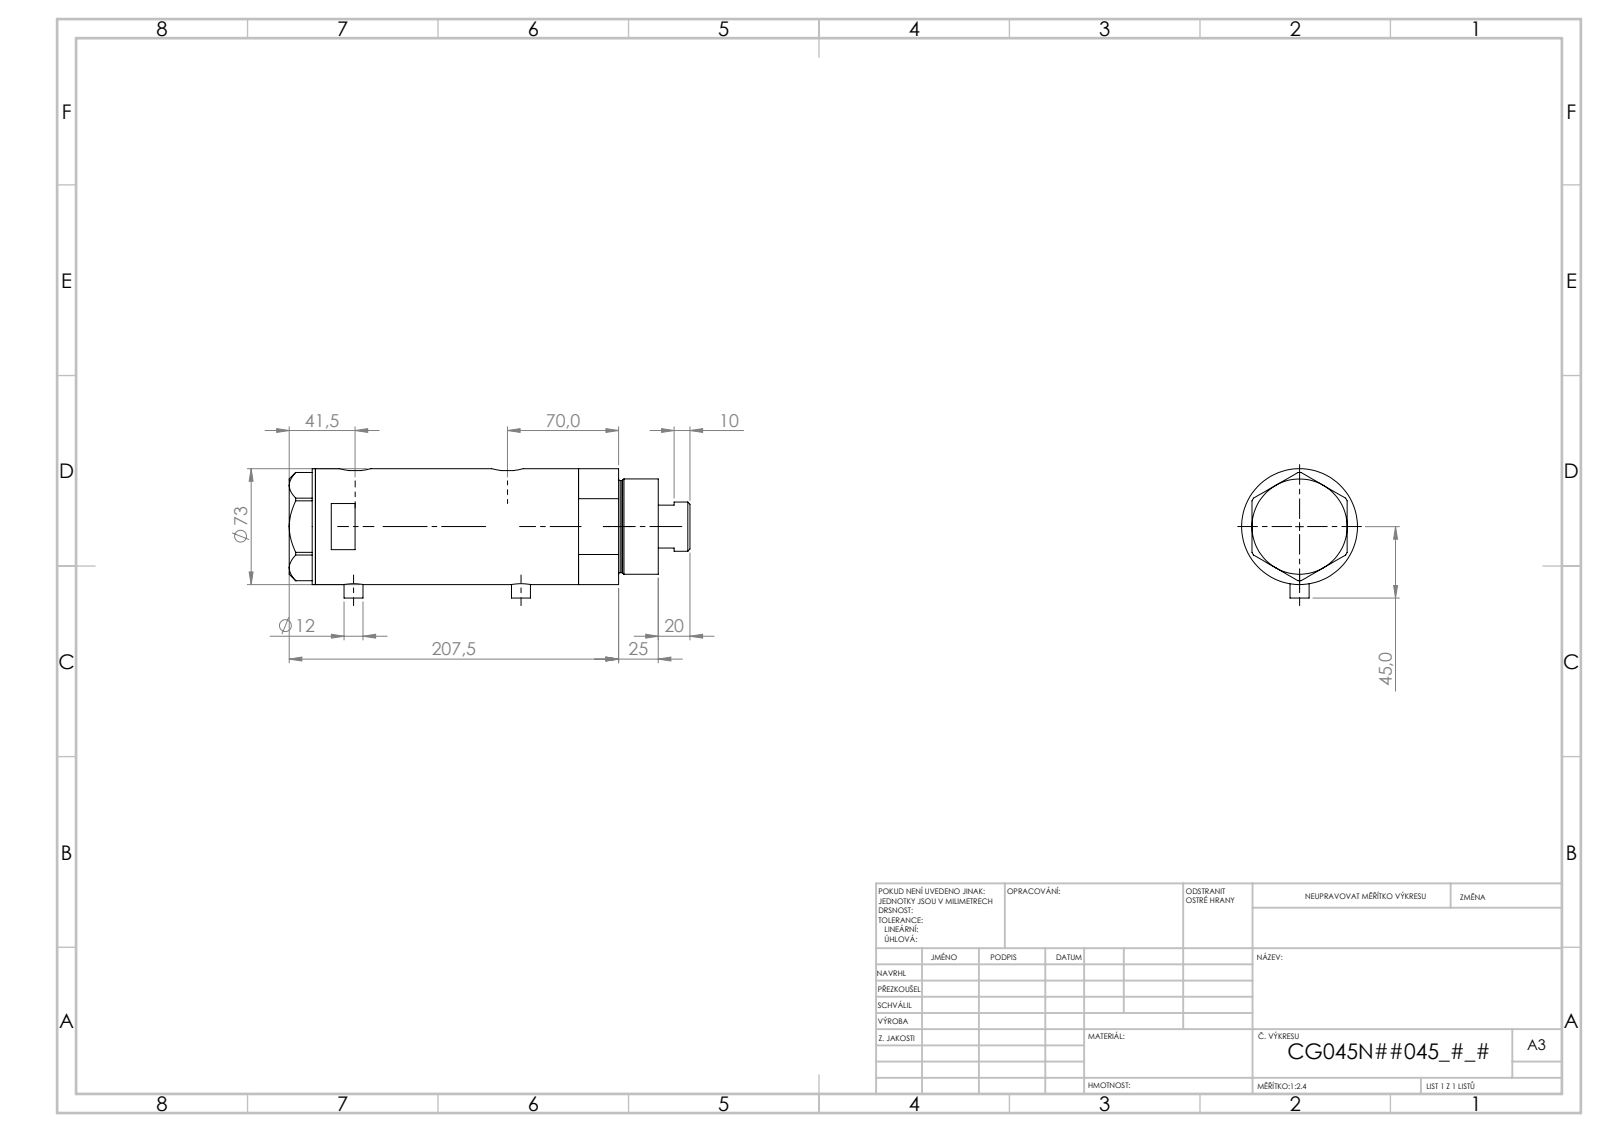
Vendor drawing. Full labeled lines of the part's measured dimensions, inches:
Part name (STEP PRODUCT): V270CG_VC; V270CG_FRONT; V270CG_MIDDLE; V270CG_BACK
STEP written by: SolidWorks 2019 (CONFIG_CONTROL_DESIGN)
Units: inches
Bodies: 4 solids, 125 faces (50 planar, 55 cylindrical, 20 other)
Overall size (bounding box): 9.312 × 2.917 × 2.874
Volume: 50.02 in³ · Surface area: 218.8 in²
Round holes (diameter × count): ⌀0.197 ×2, ⌀0.492 ×2, ⌀0.518 ×2, ⌀0.413 ×1, ⌀1.26 ×1, ⌀1.319 ×1, ⌀1.772 ×1, ⌀1.89 ×1, ⌀2.52 ×1
Round bosses / shafts (diameter × count): ⌀0.472 ×2, ⌀2.874 ×1, ⌀2.362 ×1, ⌀2.283 ×1, ⌀1.22 ×1
Partial cylindrical surfaces — rounded edges, fillets, slot ends (radius × count): R0.394 ×2
Main face-to-face distances: 4.415, 1.024, 3.391, 0.65, 1.673, 5.065, 7.874, 8.524, 6.851, 3.459
Hole centre spacings: 3.805, 0.039, 0.039, 0.335, 0.335, 3.431, 3.47, 3.47
